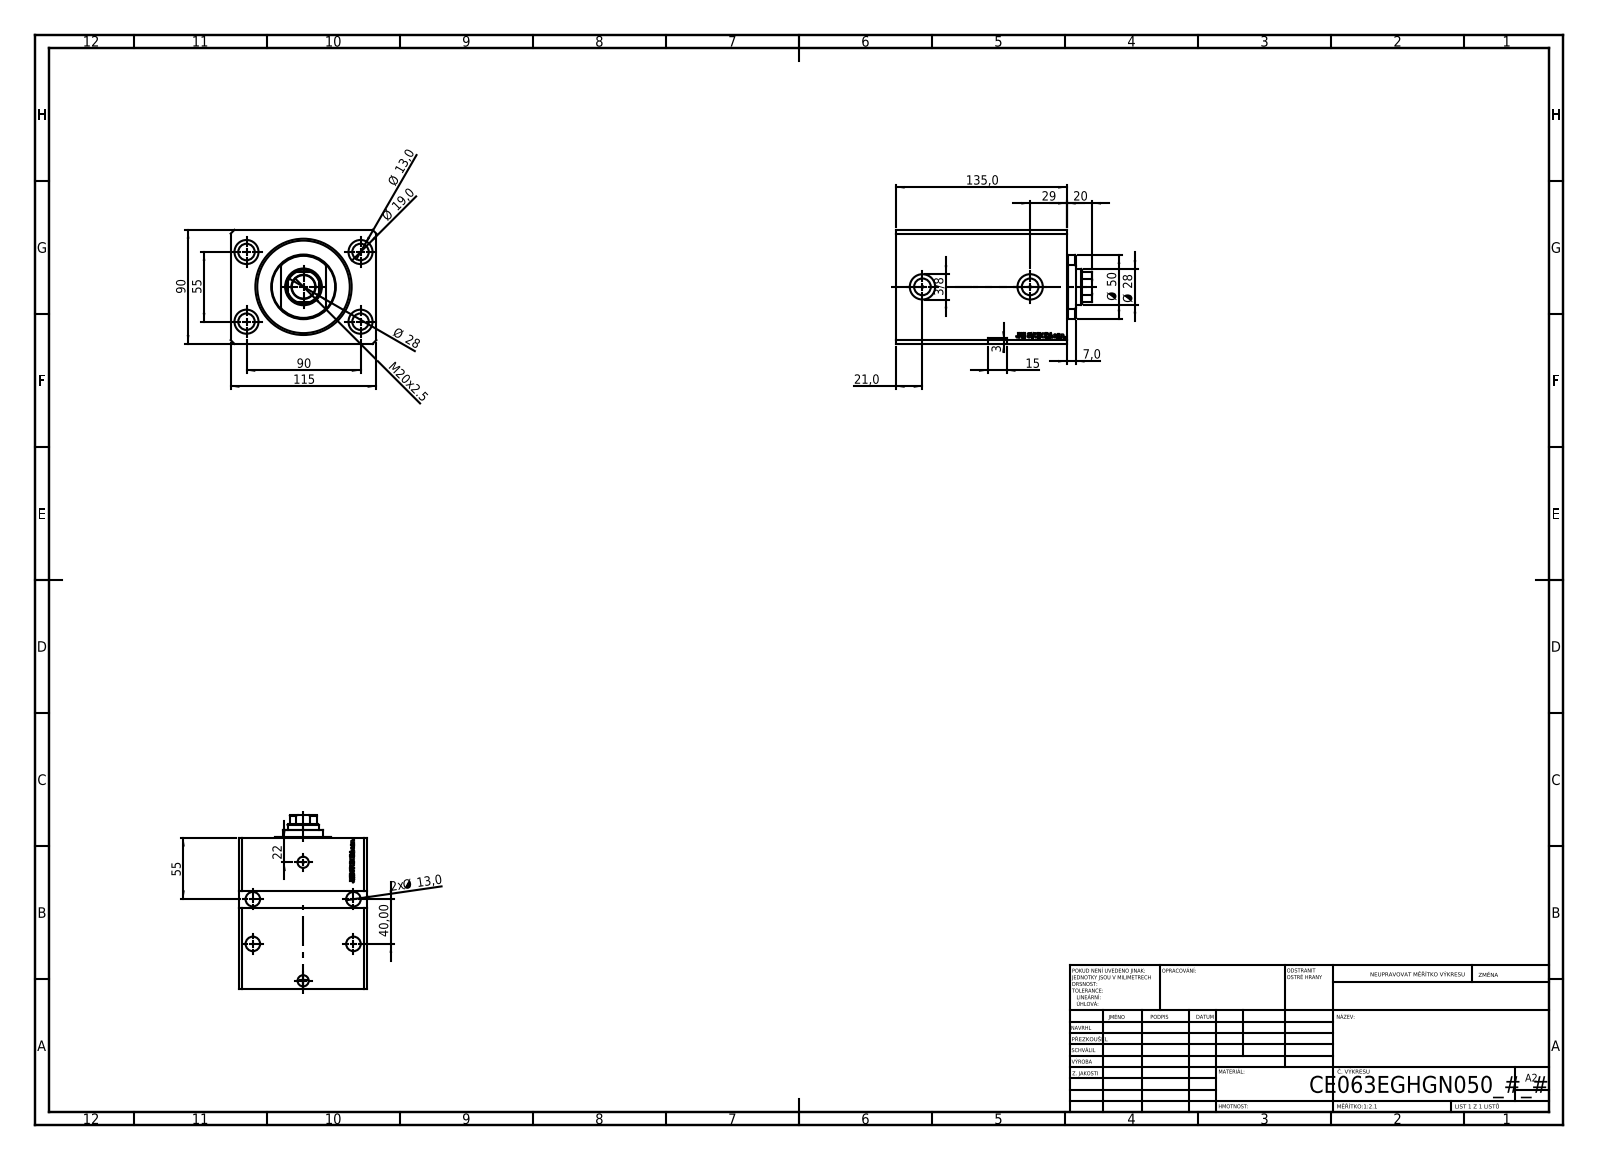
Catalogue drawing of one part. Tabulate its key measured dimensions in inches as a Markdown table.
| quantity | value |
| --- | --- |
| part name | V250CE_E_Body; V250CE_C_VCP; V250CE_VC_E |
| STEP written by | SolidWorks 2019 (CONFIG_CONTROL_DESIGN) |
| units | inches |
| bodies | 3 solids, 957 faces (467 planar, 104 cylindrical, 386 other) |
| overall size | 6.102 × 4.528 × 3.543 |
| volume | 69.81 in³ |
| surface area | 269.5 in² |
| round holes (diameter × count) | 0.512 × 8, 0.049 × 4, 0.748 × 4, 0.394 × 2, 0.518 × 2, 0.787 × 2, 0.728 × 1, 1.102 × 1, 2.48 × 1, 2.992 × 1 |
| round bosses / shafts (diameter × count) | 1.969 × 1 |
| partial cylindrical surfaces (radius × count) | 0.531 × 1 |
| main face-to-face distances | 4.528, 3.543, 5.315, 0.705, 4.61, 0.787, 3.823, 2.559, 1.854, 1.969 |
| hole center spacings | 2.076, 2.197, 3.376, 3.543, 1.575, 2.165, 2.185, 3.358 |
